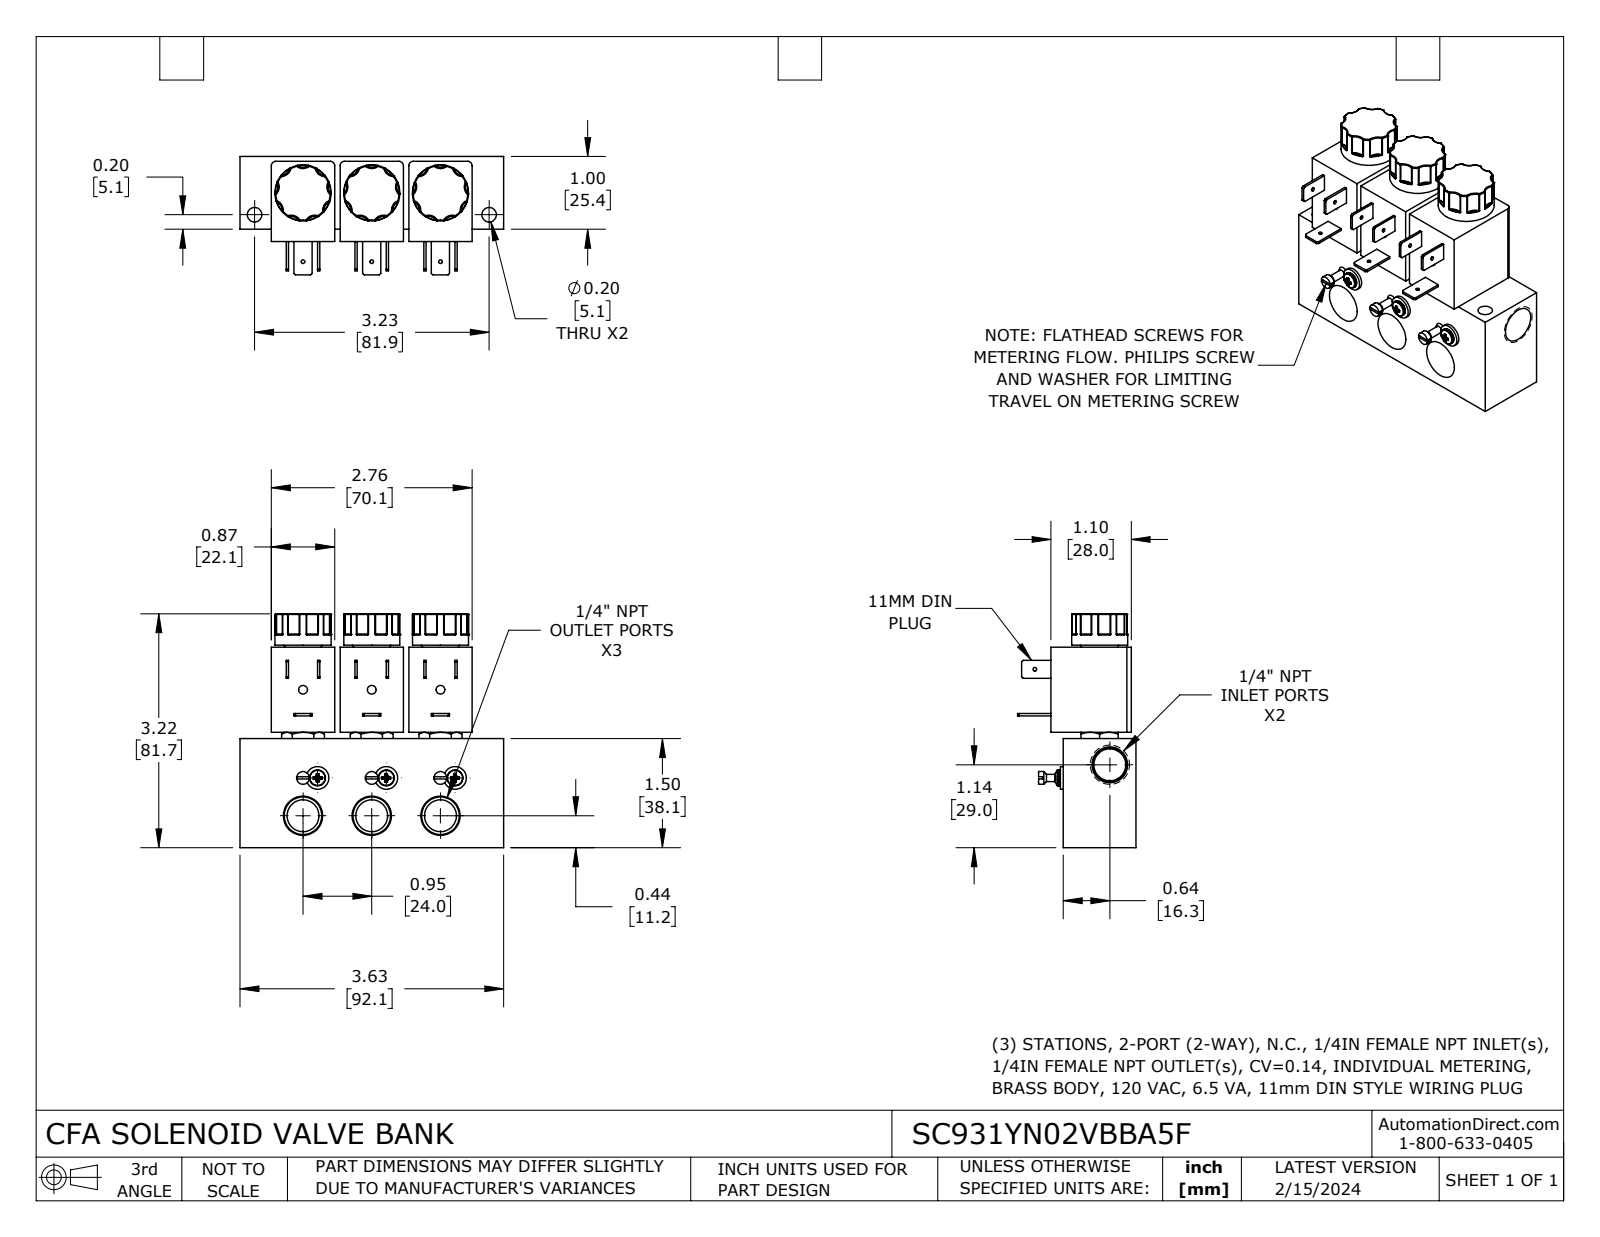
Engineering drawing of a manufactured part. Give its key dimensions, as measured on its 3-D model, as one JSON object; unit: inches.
{"part_name": "SC931YN02VBBA5F", "step_written_by": "SolidWorks 2023 (CONFIG_CONTROL_DESIGN)", "units": "inches", "bodies": {"solids": 1, "faces": 829, "planar": 215, "cylindrical": 197, "other": 417}, "overall_size": [3.625, 3.215, 1.627], "volume_in3": 8.838, "surface_area_in2": 53.67, "round_holes": [[0.05, 4], [0.438, 4], [0.12, 3], [0.2, 2]], "round_bosses_or_shafts": [[0.77, 3], [0.312, 3], [0.219, 3], [0.175, 3], [0.1, 3]], "partial_cylinders_radius": [[0.01, 54], [0.133, 27], [0.06, 6]], "face_to_face_distances": [1, 0.945, 1.169, 0.169, 1.5, 0.945, 1.89, 0.065, 0.935, 1.104], "hole_center_spacings": [0.945, 0.945, 1.732, 1.89, 1.973, 1.973, 2.564, 0.928]}
